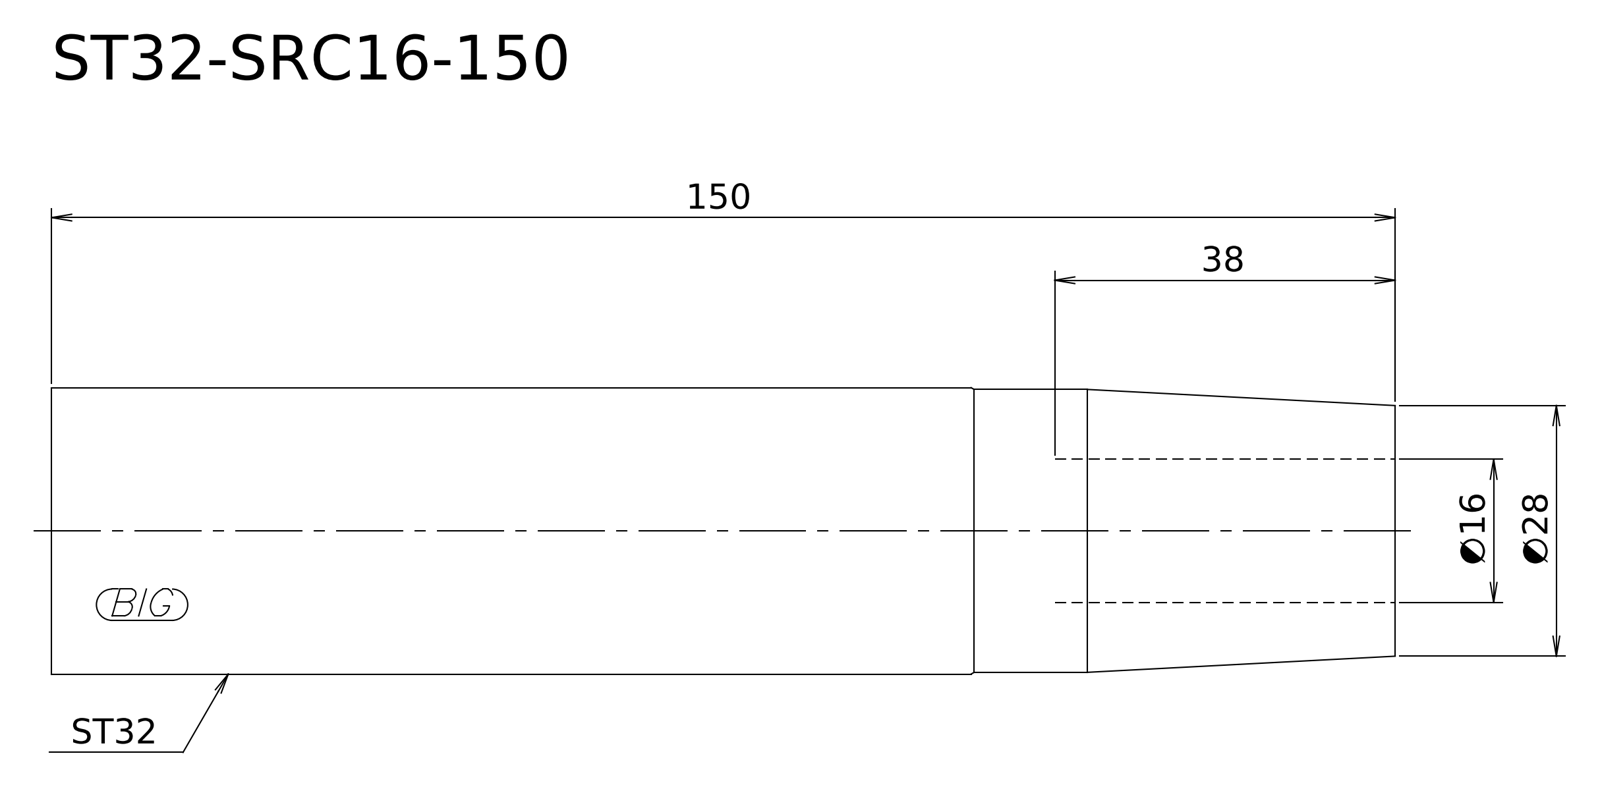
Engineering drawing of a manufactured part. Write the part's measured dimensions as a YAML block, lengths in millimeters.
step_written_by: "Kubotek KeyCreator V8.5.1 (14335) (CONFIG_CONTROL_DESIGN)"
units: millimeters
bodies: {solids: 1, faces: 6, planar: 2, cylindrical: 2, other: 2}
overall_size: [150, 32, 32]
volume: 116742
surface_area: 16256
round_bosses_or_shafts:
  - {diameter: 32, count: 1}
  - {diameter: 31.6, count: 1}
face_to_face_distances: [150]
